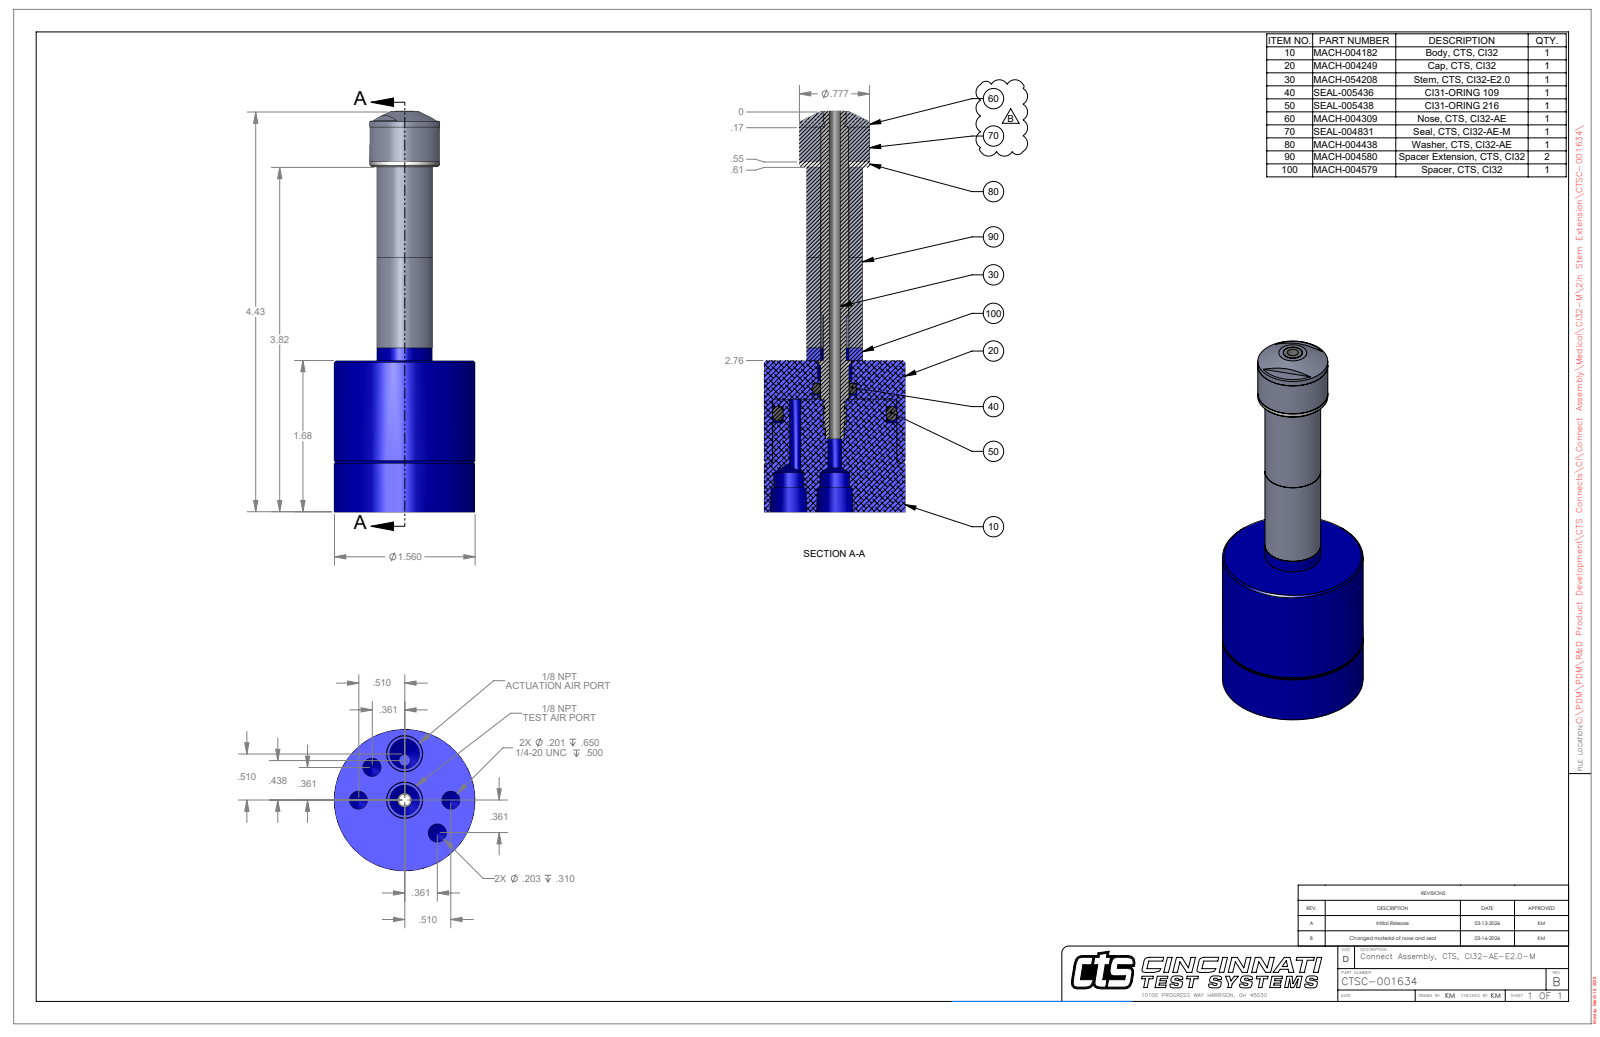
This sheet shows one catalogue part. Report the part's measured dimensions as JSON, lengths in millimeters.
{"part_name": "CTSC-001634", "step_written_by": "SolidWorks 2023 (AUTOMOTIVE_DESIGN)", "units": "millimeters", "bodies": {"solids": 7, "faces": 75, "planar": 33, "cylindrical": 27, "other": 15}, "overall_size": [112.7, 39.62, 39.62], "volume_mm3": 63735, "surface_area_mm2": 19507, "round_holes": [[5.11, 2], [5.16, 2], [8.43, 2], [3.17, 1], [3.97, 1], [5.41, 1], [7.87, 1], [7.99, 1], [9.65, 1]], "round_bosses_or_shafts": [[39.62, 1], [19.74, 1], [15.7, 1], [9.08, 1], [7.72, 1], [6.35, 1]], "partial_cylinders_radius": [[1.59, 1]], "face_to_face_distances": [42.6, 25.4, 108.17, 65.57, 98.52, 55.92, 9.65, 96.99, 54.39, 1.53], "hole_center_spacings": [12.95, 9.91, 23.93, 18.31, 25.9, 25.91]}
